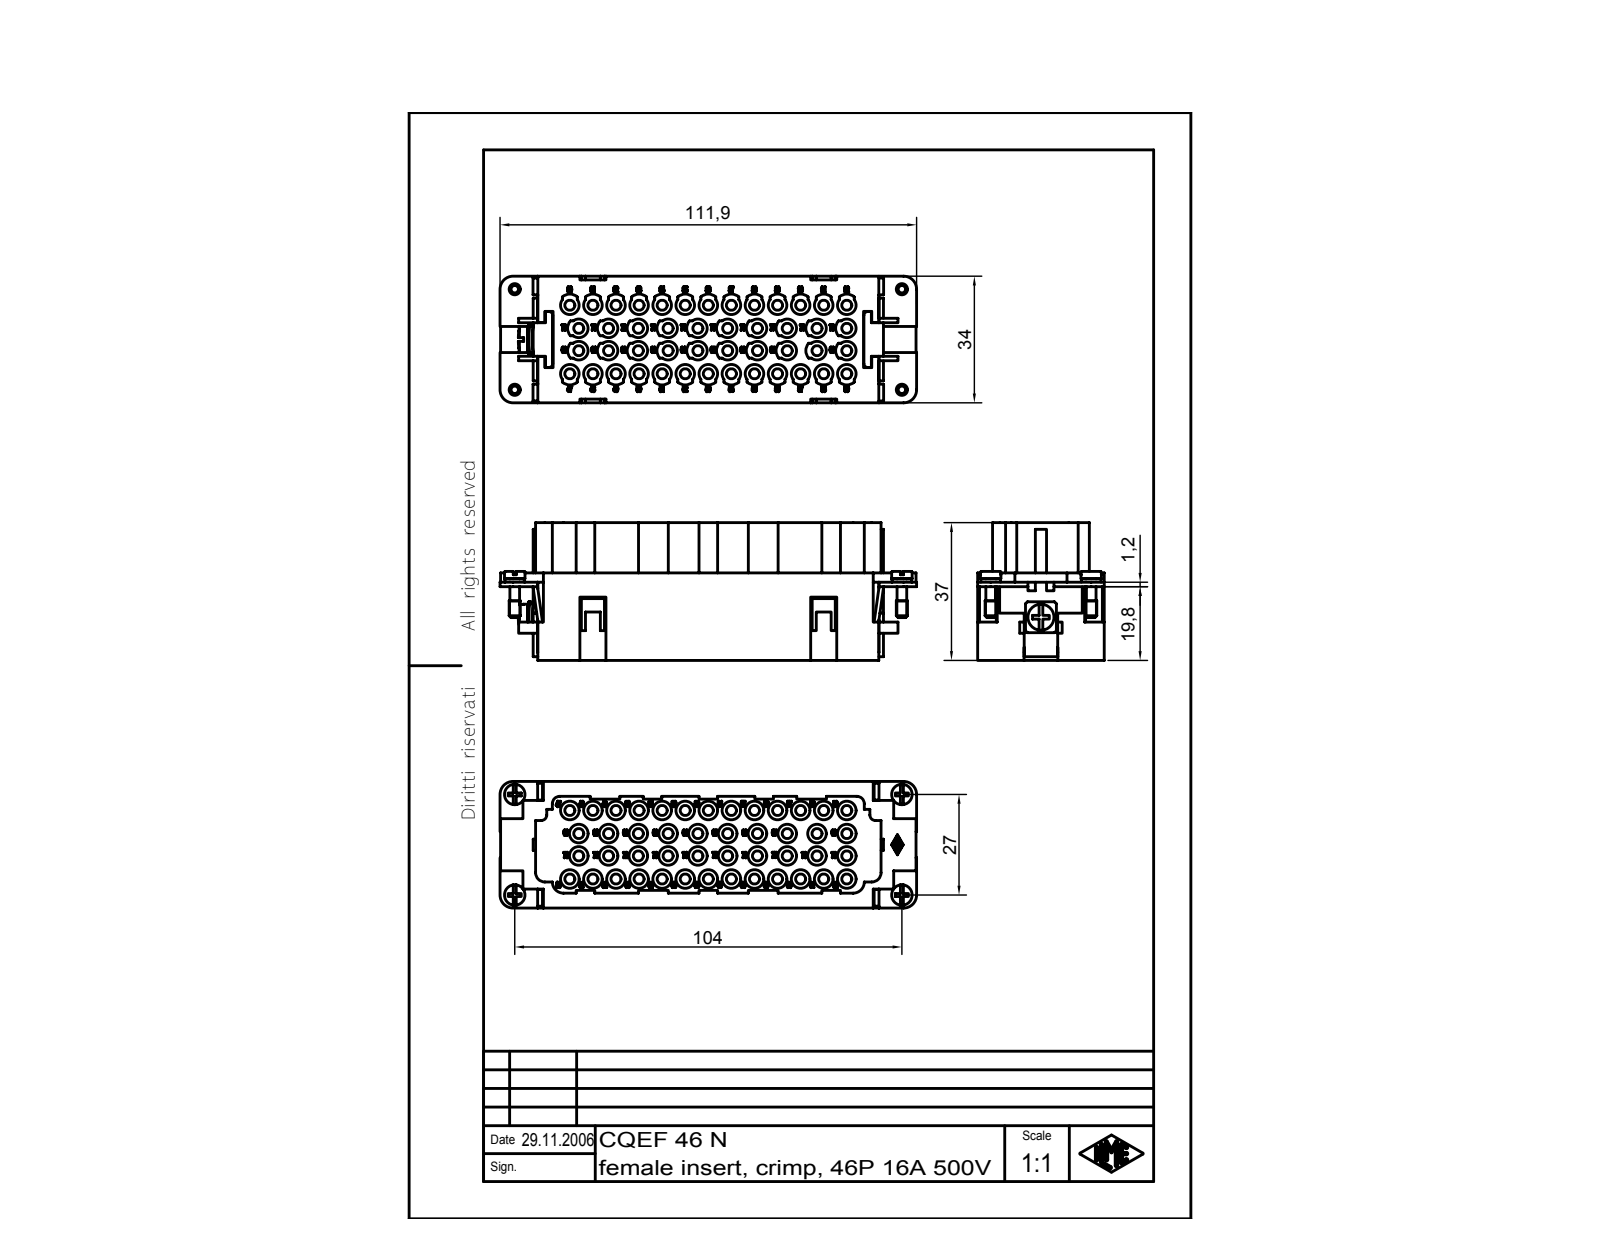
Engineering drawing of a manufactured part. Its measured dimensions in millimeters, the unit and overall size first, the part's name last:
Units: millimetres
Overall size (bounding box): 111.9 × 37 × 34
Round holes (diameter × count): ⌀3.24 ×1
Round bosses / shafts (diameter × count): ⌀5.5 ×2, ⌀5.3 ×2, ⌀3 ×2, ⌀2.6 ×2, ⌀7 ×1
Partial cylindrical surfaces — rounded edges, fillets, slot ends (radius × count): R2.5 ×25, R3 ×25, R0.1 ×14, R1 ×2, R1.5 ×2, R2 ×2, R3.5 ×2, R5.5 ×1
Main face-to-face distances: 34, 4, 37, 30, 23.5, 13.5, 4.75, 29.25, 0.75, 25.25
Volume: 77 831 mm³ · Surface area: 44 126 mm²
Bodies: 2 solids, 3710 faces (1328 planar, 123 cylindrical, 2259 other)
Part name (STEP PRODUCT): CQEF 46 N
STEP written by: Autodesk Inventor 7 (AUTOMOTIVE_DESIGN)
